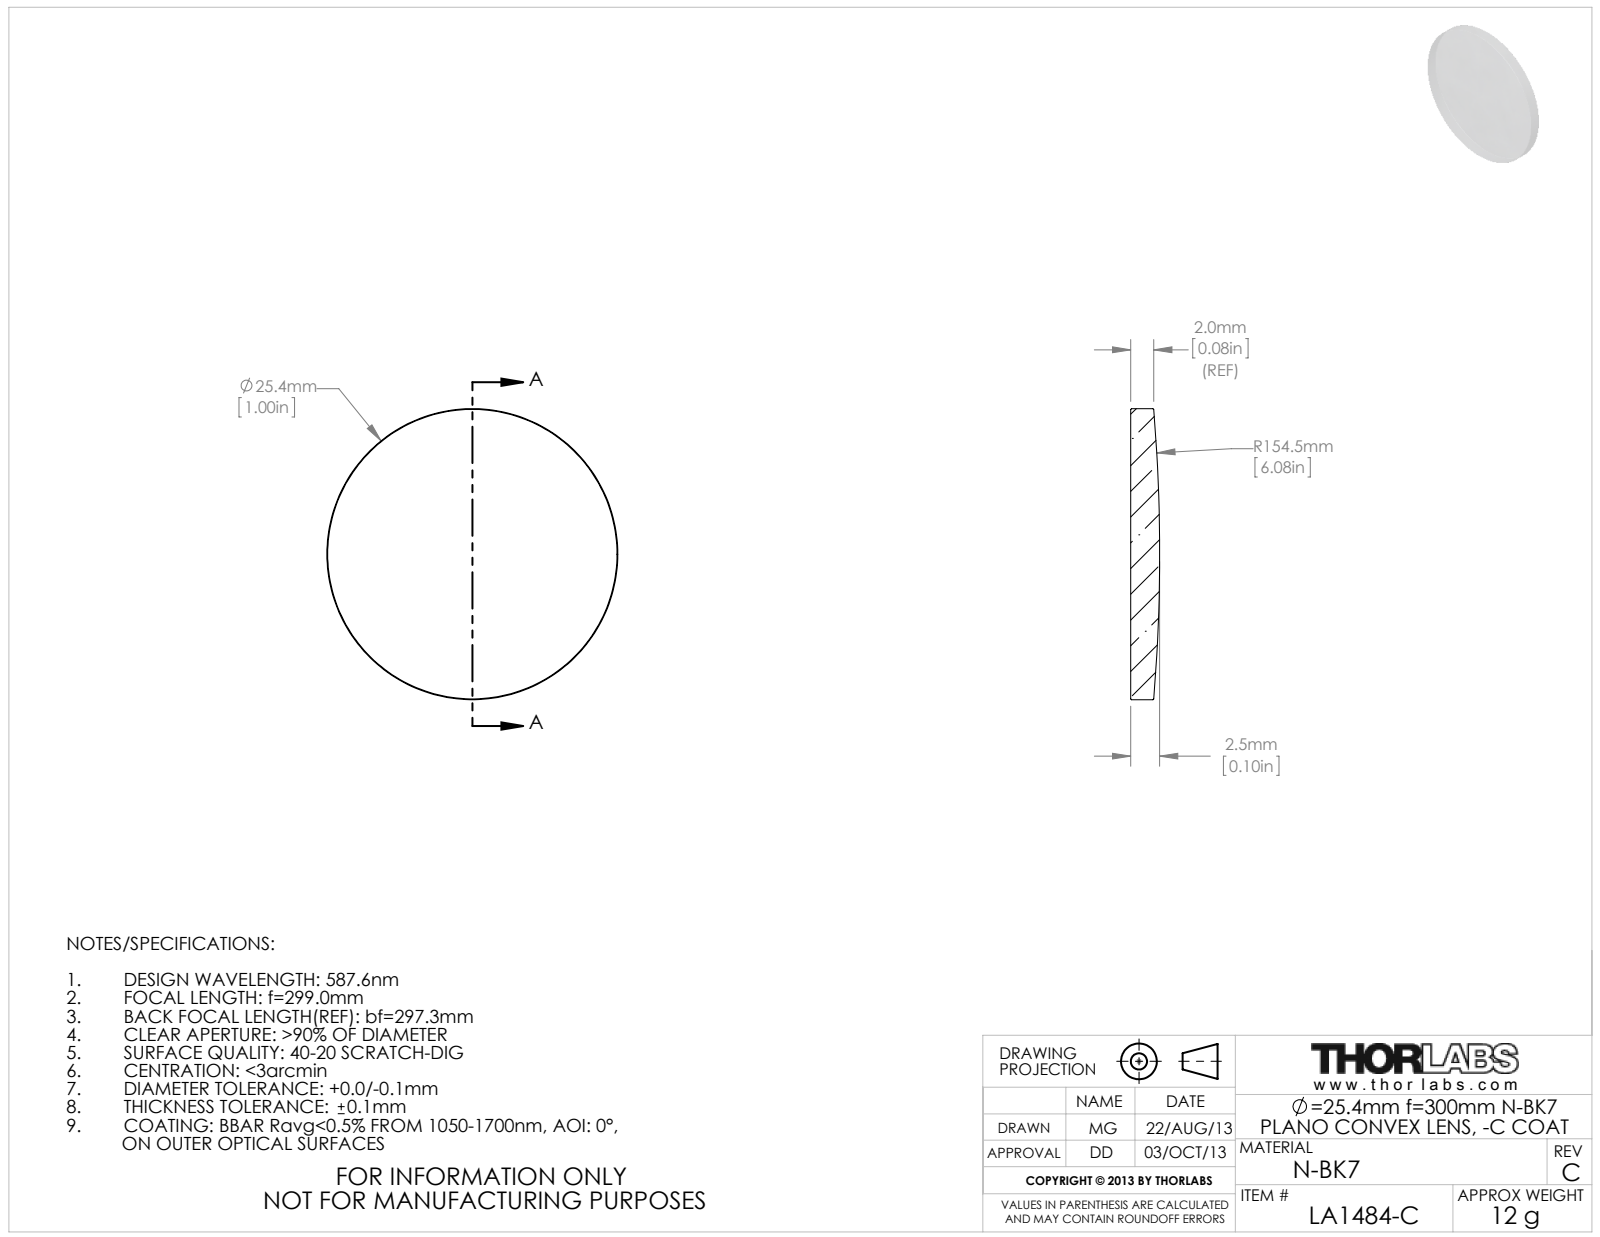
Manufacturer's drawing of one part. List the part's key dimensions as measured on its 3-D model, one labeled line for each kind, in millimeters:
Part name (STEP PRODUCT): 4590-E0W
STEP written by: SolidWorks 2009 (AUTOMOTIVE_DESIGN)
Units: millimetres
Bodies: 1 solid, 5 faces (1 planar, 2 cylindrical, 2 other)
Overall size (bounding box): 25.4 × 25.4 × 2.52
Volume: 1 145 mm³ · Surface area: 1 174 mm²
Round bosses / shafts (diameter × count): ⌀25.4 ×1
